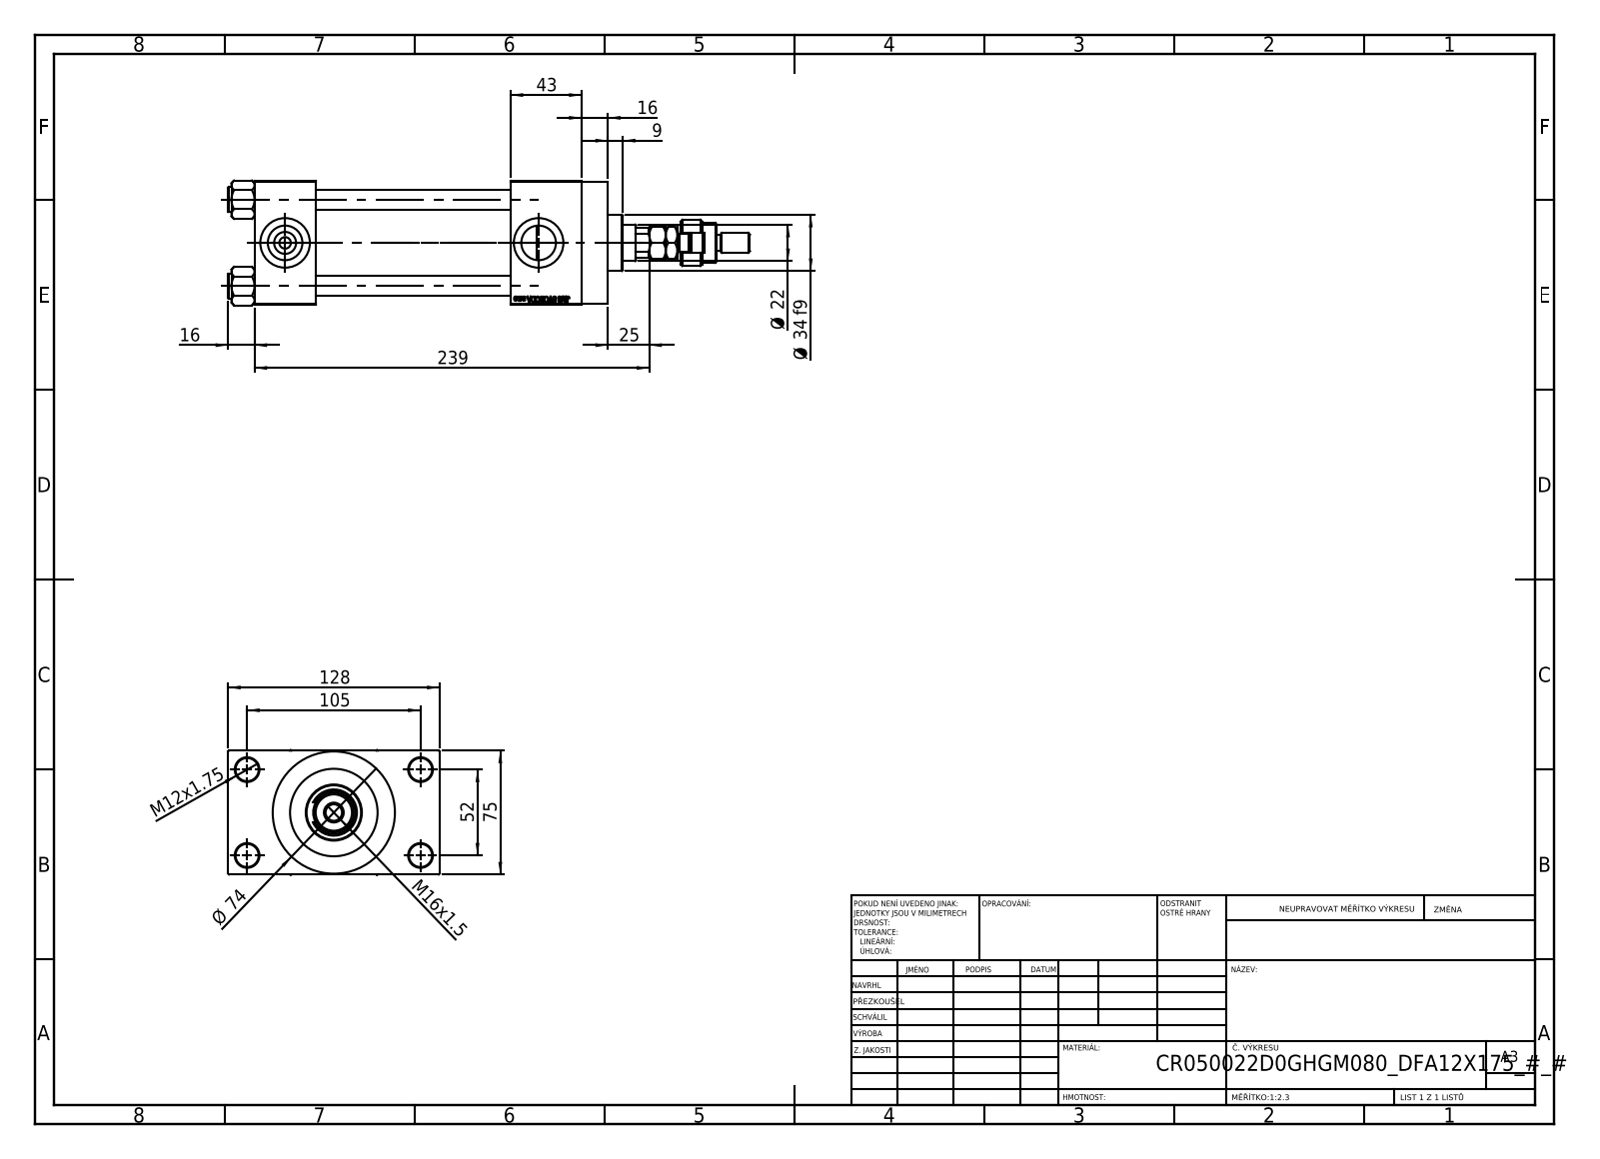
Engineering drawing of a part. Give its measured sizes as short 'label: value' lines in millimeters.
name: V215CR_D_TYCINKA; NUT_M5_D; MFA; V215CR_D_Body (+3 more)
written by: SolidWorks 2019 (CONFIG_CONTROL_DESIGN)
unit: mm
bodies: 13 solids, 1188 faces (525 planar, 101 cylindrical, 562 other)
size: 316 × 128 × 75.54
volume: 895 320 mm³; area: 206 984 mm²
holes: 4× ⌀12, 4× ⌀14, 2× ⌀7, 2× ⌀20.96, 2× ⌀30, 1× ⌀10.5, 1× ⌀22, 1× ⌀25, 1× ⌀41, 1× ⌀50, 1× ⌀53
bosses: 4× ⌀15, 1× ⌀74, 1× ⌀56, 1× ⌀34, 1× ⌀28, 1× ⌀24, 1× ⌀18, 1× ⌀12
rounds: 1× R9.75, 1× R10.5
face distances: 75, 118, 37, 155, 26.5, 198, 161, 43, 16, 101.5
hole spacings: 26.35, 36.98, 52.3, 58.43, 58.59, 78.65, 94.37, 52
